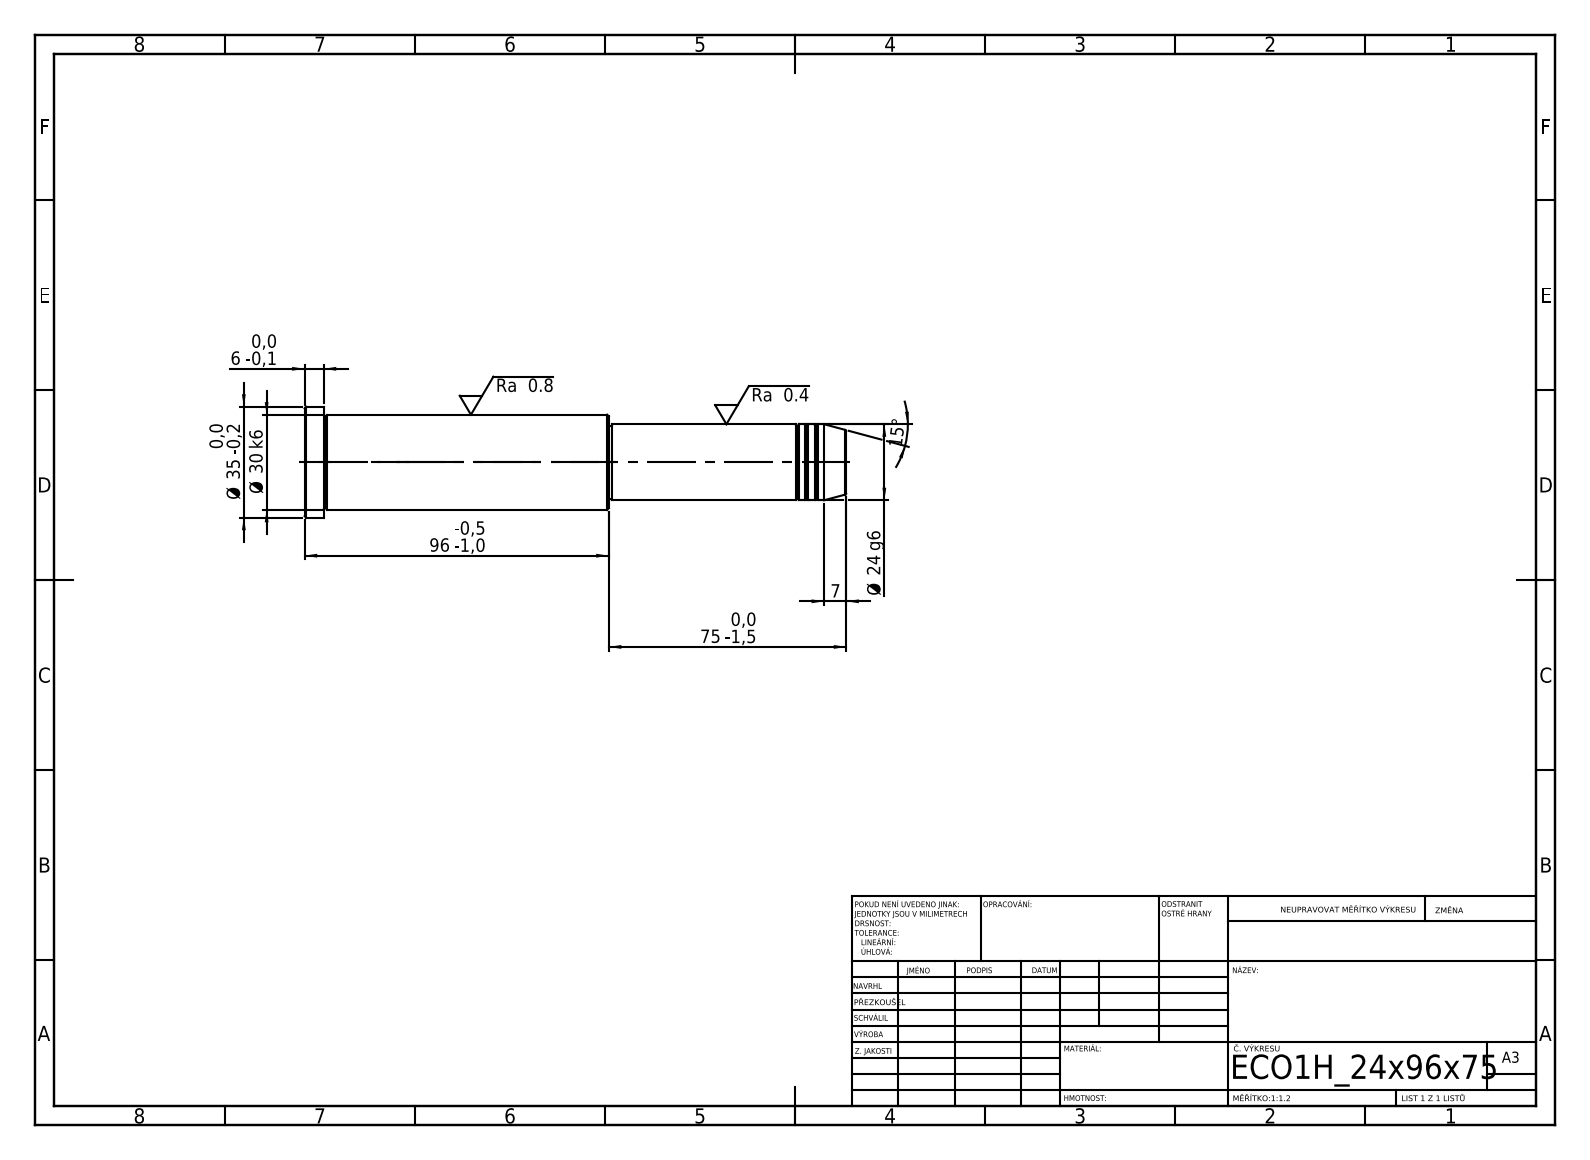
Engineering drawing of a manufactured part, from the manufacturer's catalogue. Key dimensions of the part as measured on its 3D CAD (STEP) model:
STEP written by: SolidWorks 2019 (CONFIG_CONTROL_DESIGN)
Units: millimetres
Bodies: 1 solid, 43 faces (5 planar, 14 cylindrical, 24 other)
Overall size (bounding box): 171 × 35 × 35
Volume: 102 662 mm³ · Surface area: 16 740 mm²
Round bosses / shafts (diameter × count): ⌀35 ×1, ⌀30 ×1, ⌀24 ×1, ⌀23 ×1
Main face-to-face distances: 171, 165, 6, 75, 90, 96, 74, 1, 91, 97
